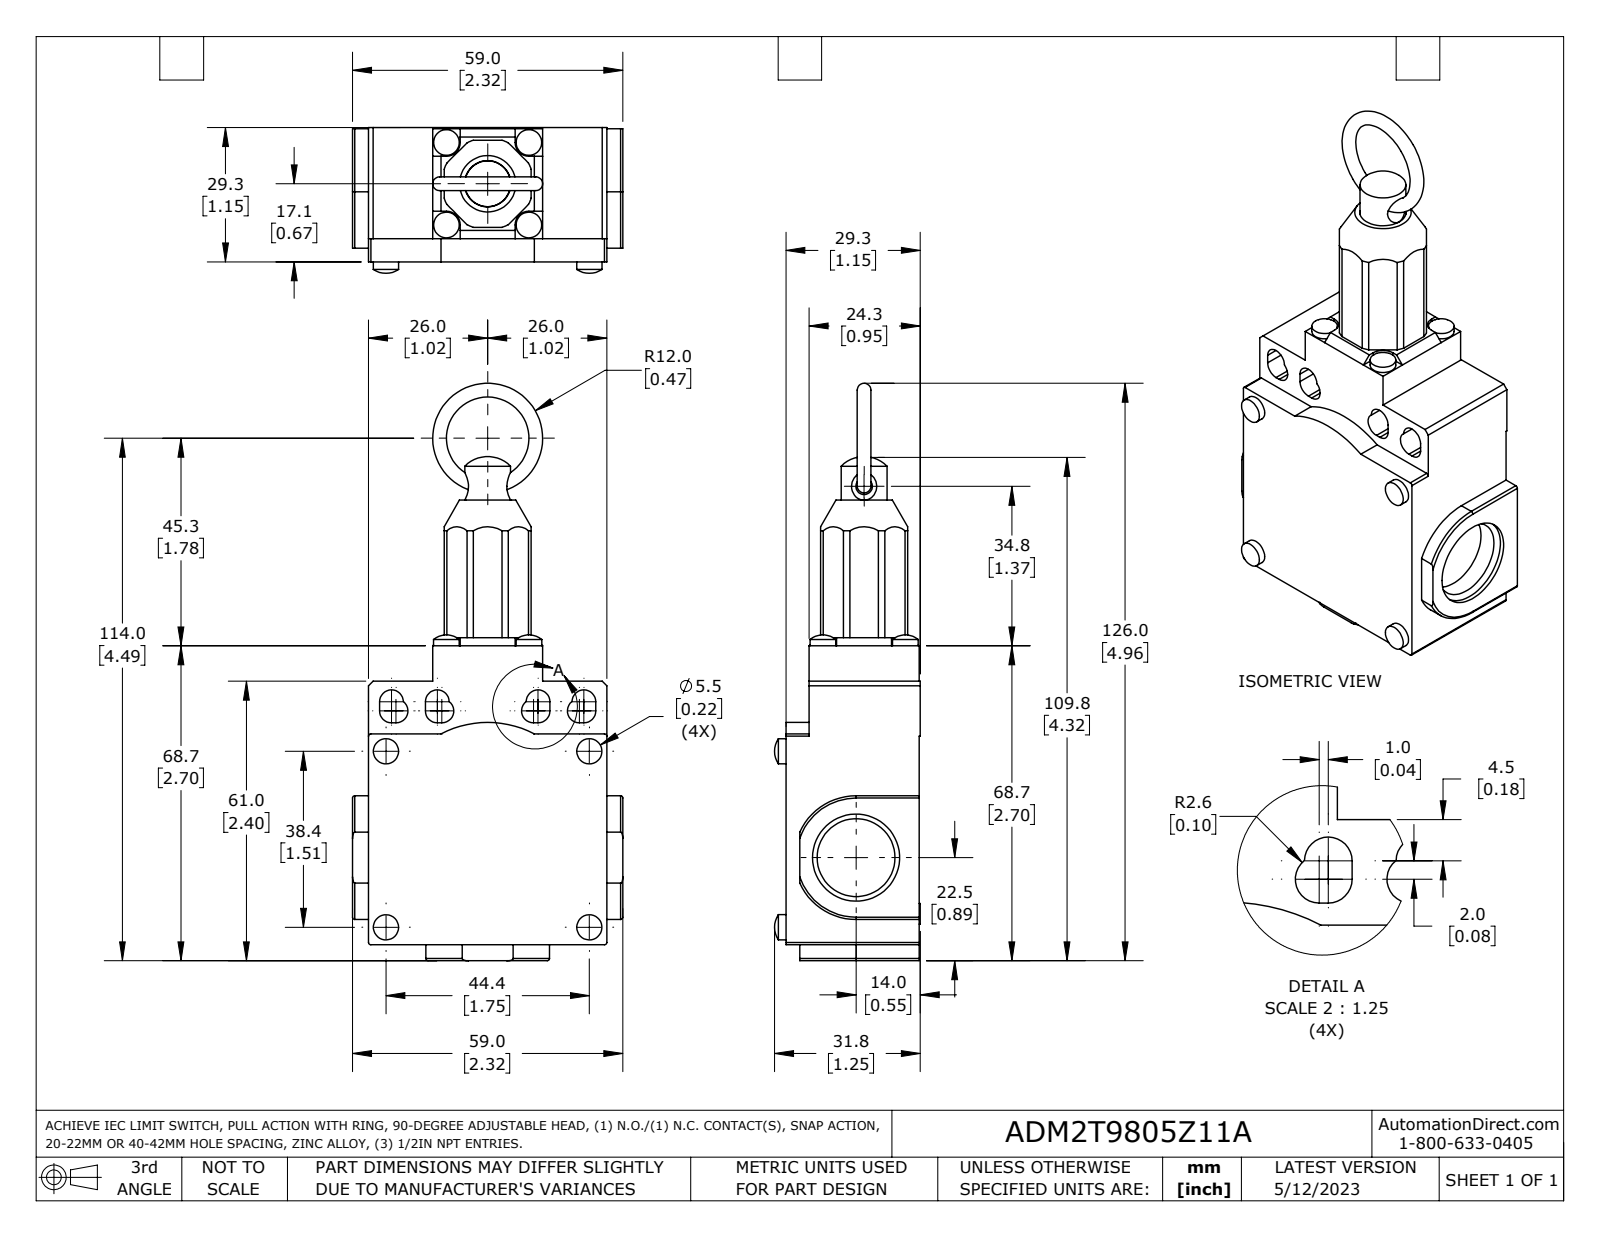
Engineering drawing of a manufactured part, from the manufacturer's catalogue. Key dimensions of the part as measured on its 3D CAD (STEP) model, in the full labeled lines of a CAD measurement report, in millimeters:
Part name (STEP PRODUCT): ADM2T9805Z11A
STEP written by: SolidWorks 2021 (AUTOMOTIVE_DESIGN)
Units: millimetres
Bodies: 1 solid, 182 faces (91 planar, 69 cylindrical, 22 other)
Overall size (bounding box): 126 × 59 × 31.8
Volume: 97 400 mm³ · Surface area: 22 080 mm²
Round holes (diameter × count): ⌀17 ×2, ⌀19 ×2, ⌀10.1 ×1, ⌀15 ×1
Round bosses / shafts (diameter × count): ⌀5.6 ×4, ⌀5.5 ×4, ⌀14.9 ×1, ⌀10 ×1, ⌀3.6 ×1
Partial cylindrical surfaces — rounded edges, fillets, slot ends (radius × count): R2.6 ×12, R0.5 ×10, R3 ×4, R13.5 ×2, R10 ×1, R10.2 ×1, R22 ×1
Main face-to-face distances: 29.1, 2.5, 3.5, 52, 6, 24, 14, 35.5, 29.3, 55.5
Hole centre spacings: 1.8
